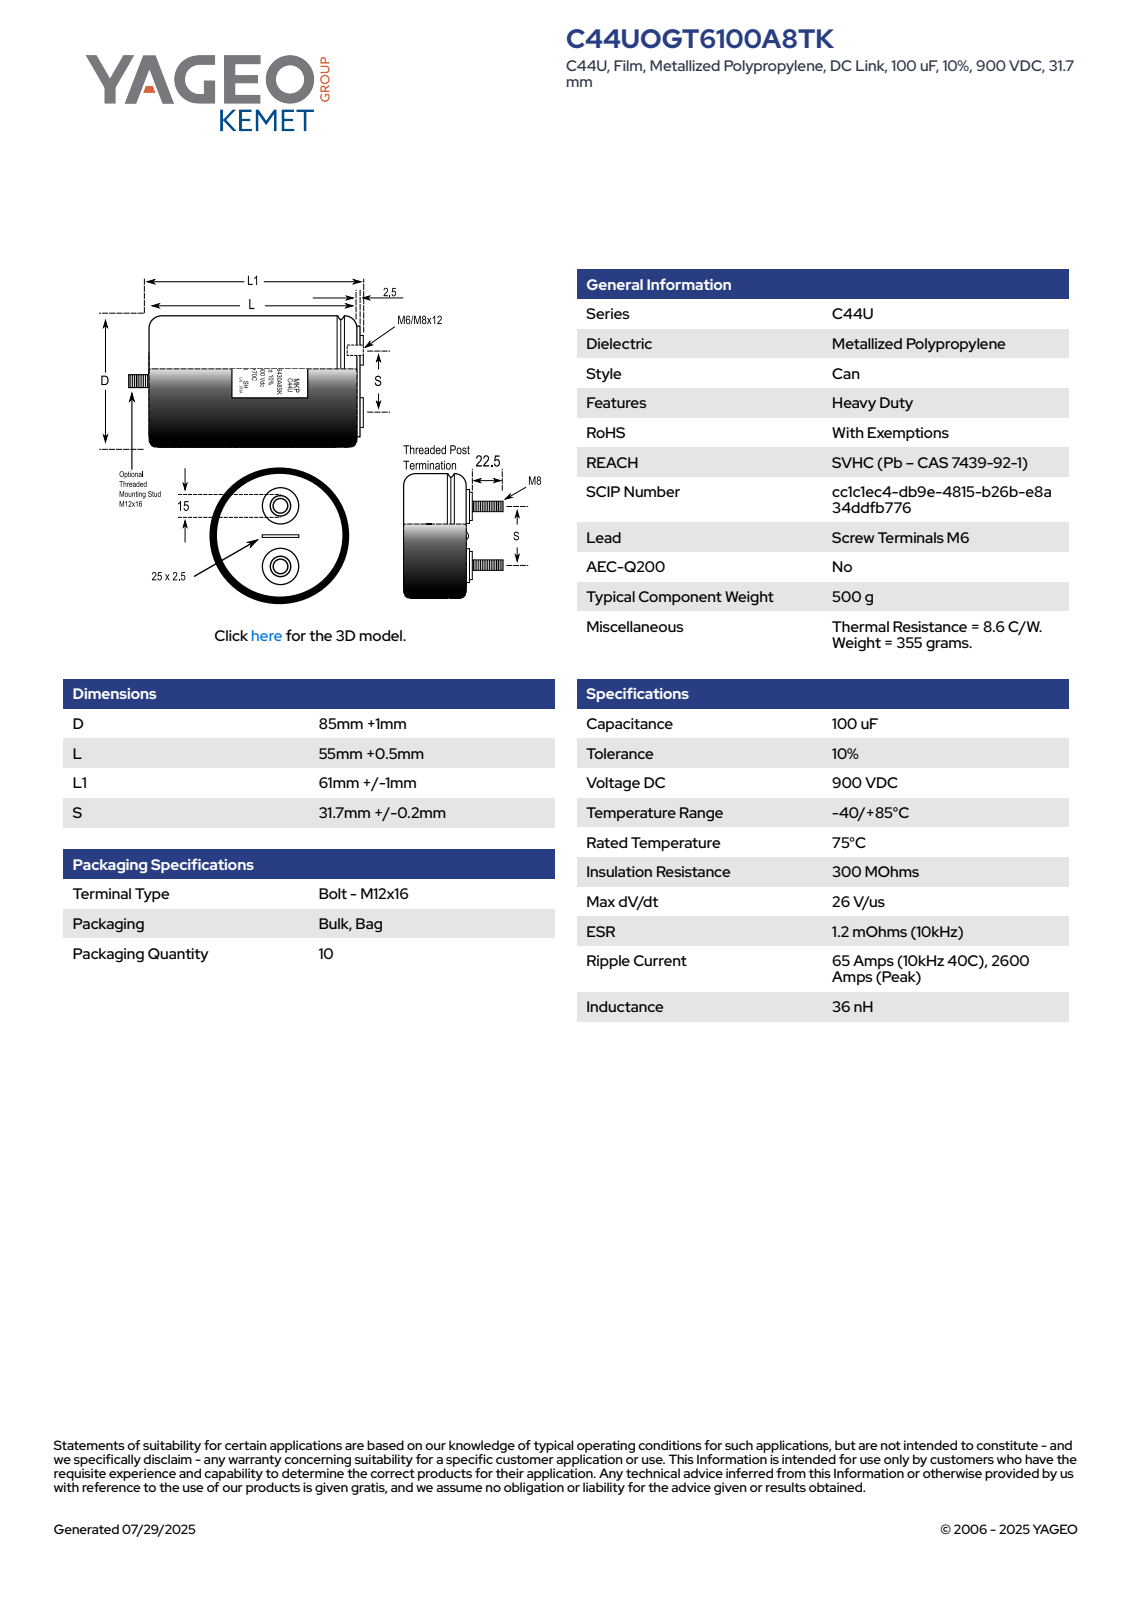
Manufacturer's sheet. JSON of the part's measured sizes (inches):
{"part_name": "CFP_C44U_T_85X55_D86L55.5S31.9", "step_written_by": "SolidWorks 2021 (AUTOMOTIVE_DESIGN)", "units": "inches", "bodies": {"solids": 1, "faces": 104, "planar": 36, "cylindrical": 29, "other": 39}, "overall_size": [3.386, 3.386, 2.913], "volume_in3": 19.33, "surface_area_in2": 40.84, "round_holes": [[0.236, 2]], "round_bosses_or_shafts": [[0.709, 2], [0.591, 2], [3.386, 1], [2.756, 1], [0.472, 1]], "partial_cylinders_radius": [[1.693, 1]], "face_to_face_distances": [2.185, 0.098, 0.049, 2.283, 2.234, 0.63, 2.815, 2.864, 2.913, 2.894], "hole_center_spacings": [1.256]}
